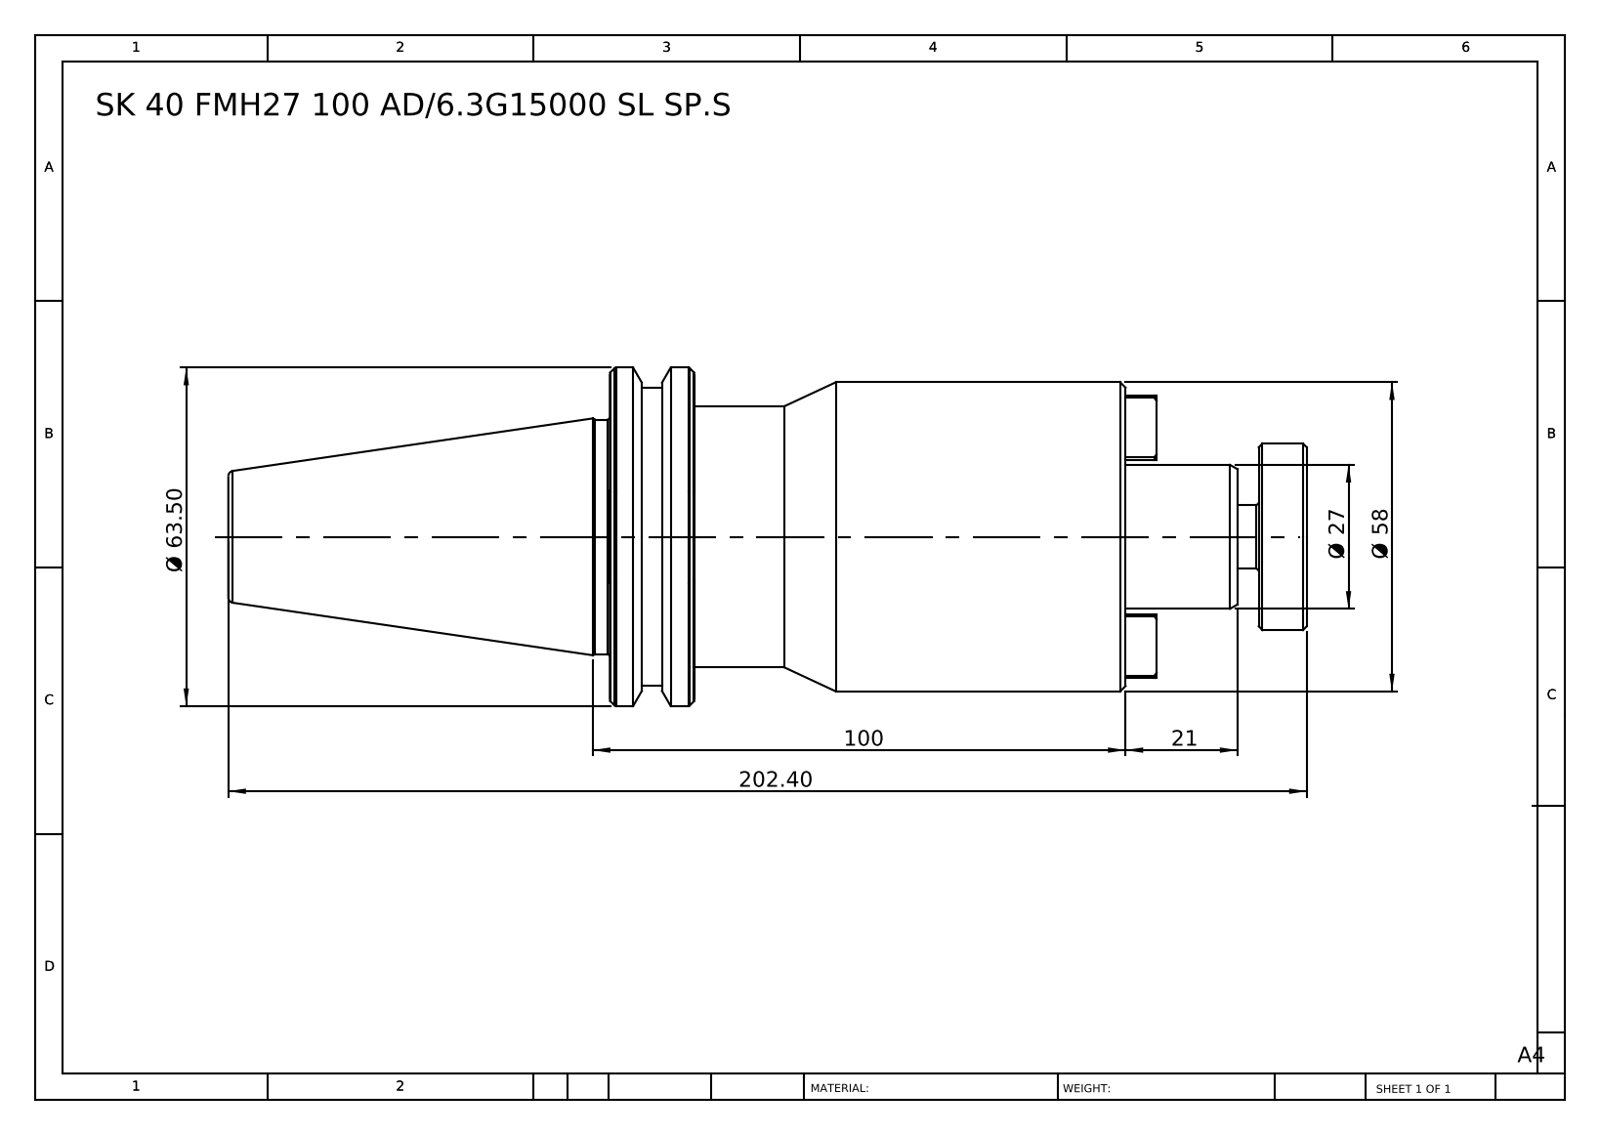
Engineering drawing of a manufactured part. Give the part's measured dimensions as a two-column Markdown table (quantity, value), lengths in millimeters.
| quantity | value |
| --- | --- |
| part name | SK40 FMH27 100 AD-6.3G15000 SL SP.S |
| STEP written by | SolidWorks 2014 (CONFIG_CONTROL_DESIGN) |
| units | millimeters |
| bodies | 1 solid, 105 faces (35 planar, 18 cylindrical, 52 other) |
| overall size | 202.4 × 63.5 × 63.5 |
| volume | 336 978 mm³ |
| surface area | 36 883 mm² |
| round bosses / shafts (diameter × count) | 63.5 × 1, 58 × 1, 56 × 1, 49 × 1, 44 × 1, 35 × 1, 27 × 1, 12 × 1 |
| main face-to-face distances | 96.8, 80.9, 15.9, 34, 114.9, 130.8, 9, 25, 105.9, 121.8 |
